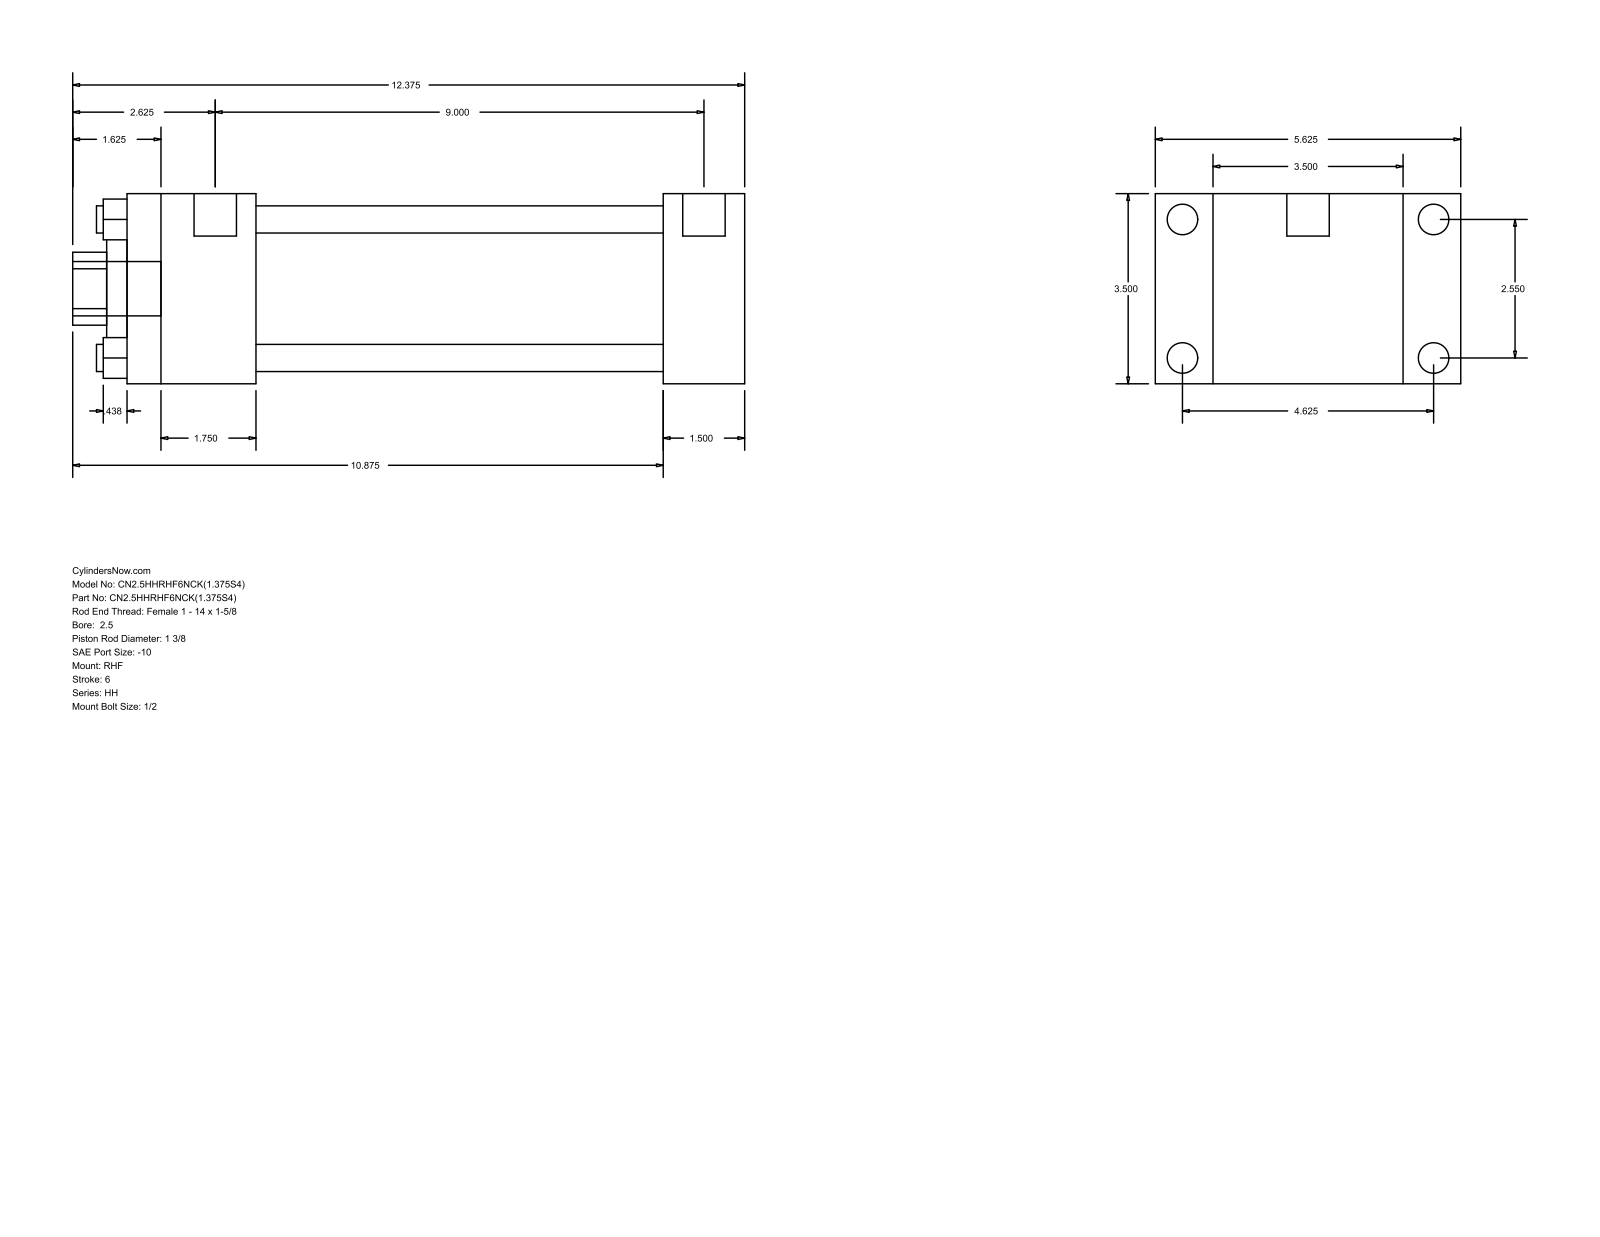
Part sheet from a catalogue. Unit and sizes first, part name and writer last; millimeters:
Units: millimetres
Overall size (bounding box): 314.32 × 142.88 × 88.9
Round holes (diameter × count): ⌀12.7 ×4, ⌀34.92 ×1, ⌀50.8 ×1, ⌀73.03 ×1
Round bosses / shafts (diameter × count): ⌀14.3 ×4, ⌀5.56 ×4, ⌀19.84 ×2, ⌀25.4 ×1
Partial cylindrical surfaces — rounded edges, fillets, slot ends (radius × count): R17.06 ×1
Main face-to-face distances: 88.9, 38.09, 26.99, 115.89, 250.83, 288.92, 142.88, 60.32, 190.51, 228.6
Hole centre spacings: 45.79, 64.76, 91.58
Bodies: 0 solids, 88 faces (60 planar, 28 cylindrical, 0 other)
Part name (STEP PRODUCT): HH_RHF__0250_1.375
STEP written by: GSSL Pune (CONFIG_CONTROL_DESIGN)
